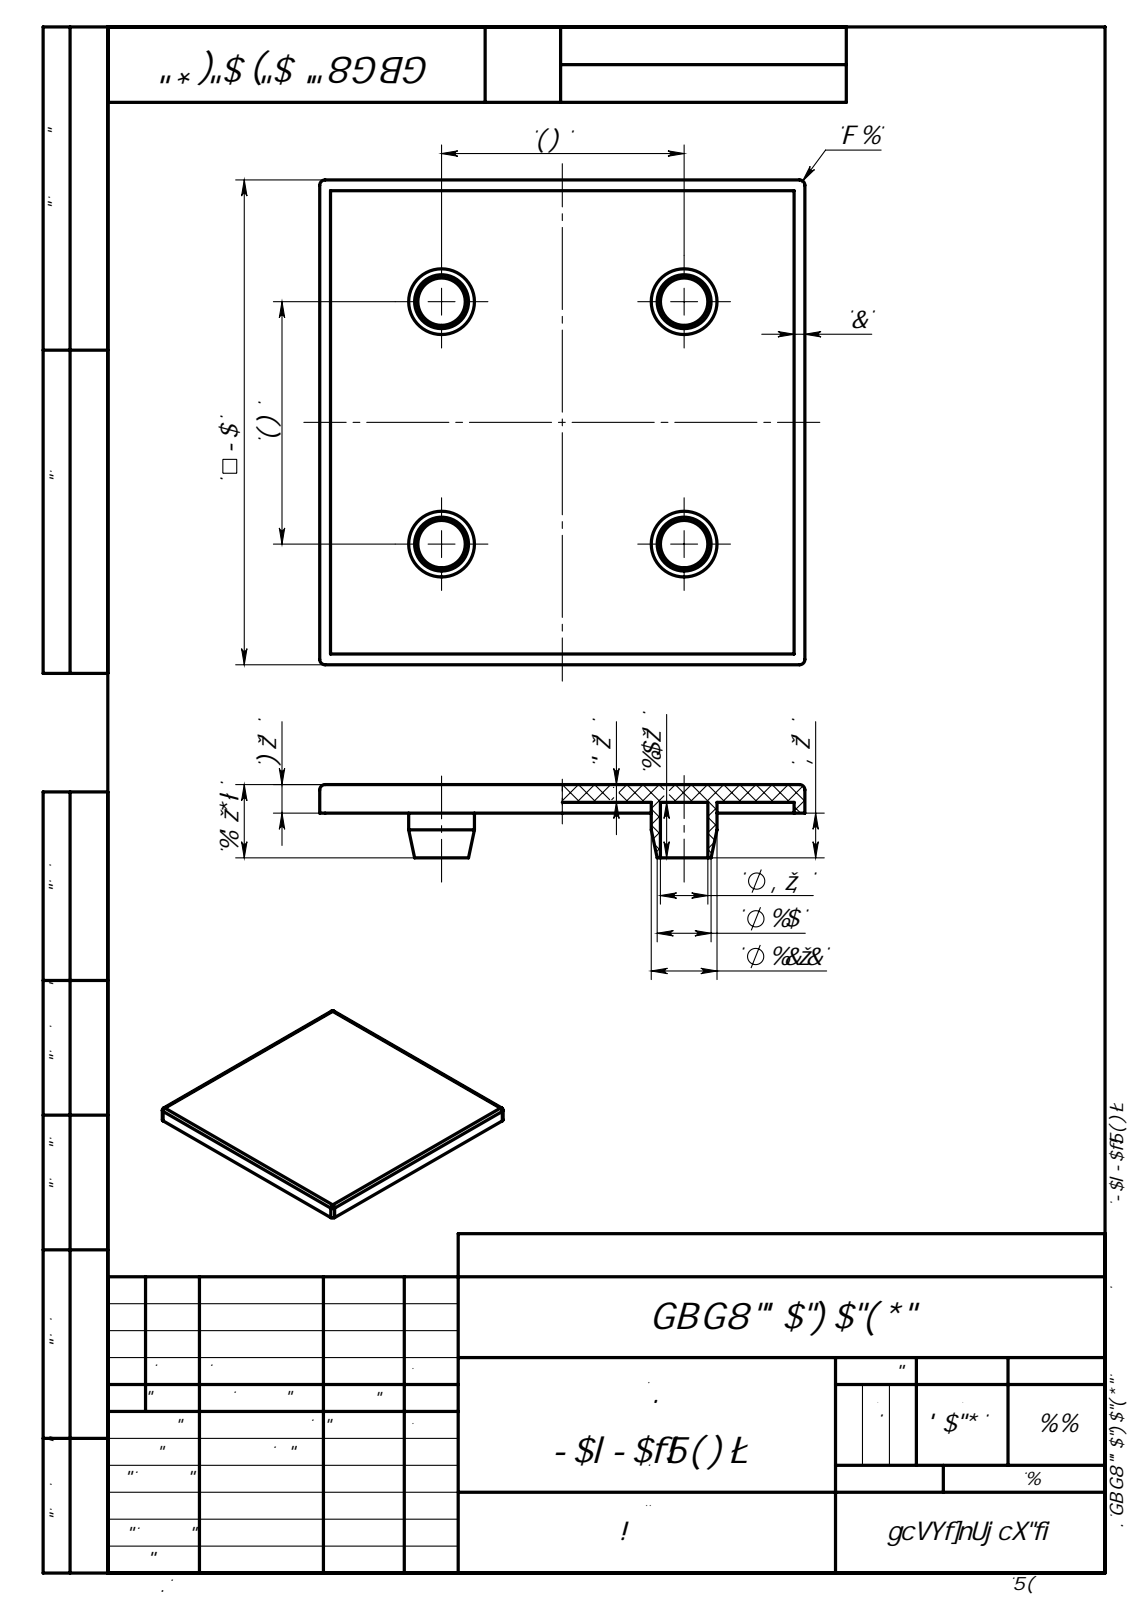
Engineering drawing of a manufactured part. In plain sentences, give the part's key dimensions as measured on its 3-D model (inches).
The part is named "SNSD.30.50.46. Заглушка торцевая 90x90(A45)". Its 3-D file was written by "SolidWorks 2016 (AUTOMOTIVE_DESIGN)". It is 1 solid with 55 faces: 19 planar, 24 cylindrical and 12 other. Overall it measures 3.543 by 3.543 by 0.535 inches. Its volume is 1.828 cubic inches and its surface area 32.77 square inches. Round holes: 4 of diameter 0.346. Round bosses or shafts: 4 of diameter 0.48. Partial cylindrical surfaces (rounded edges, fillets, slot ends): 8 of radius 0.039. The main face-to-face distances are 0.13, 0.079, 3.543, 0.209, 3.465, 3.386, 0.327, 0.406, 0.535. The hole center spacings are 1.772, 2.506.
